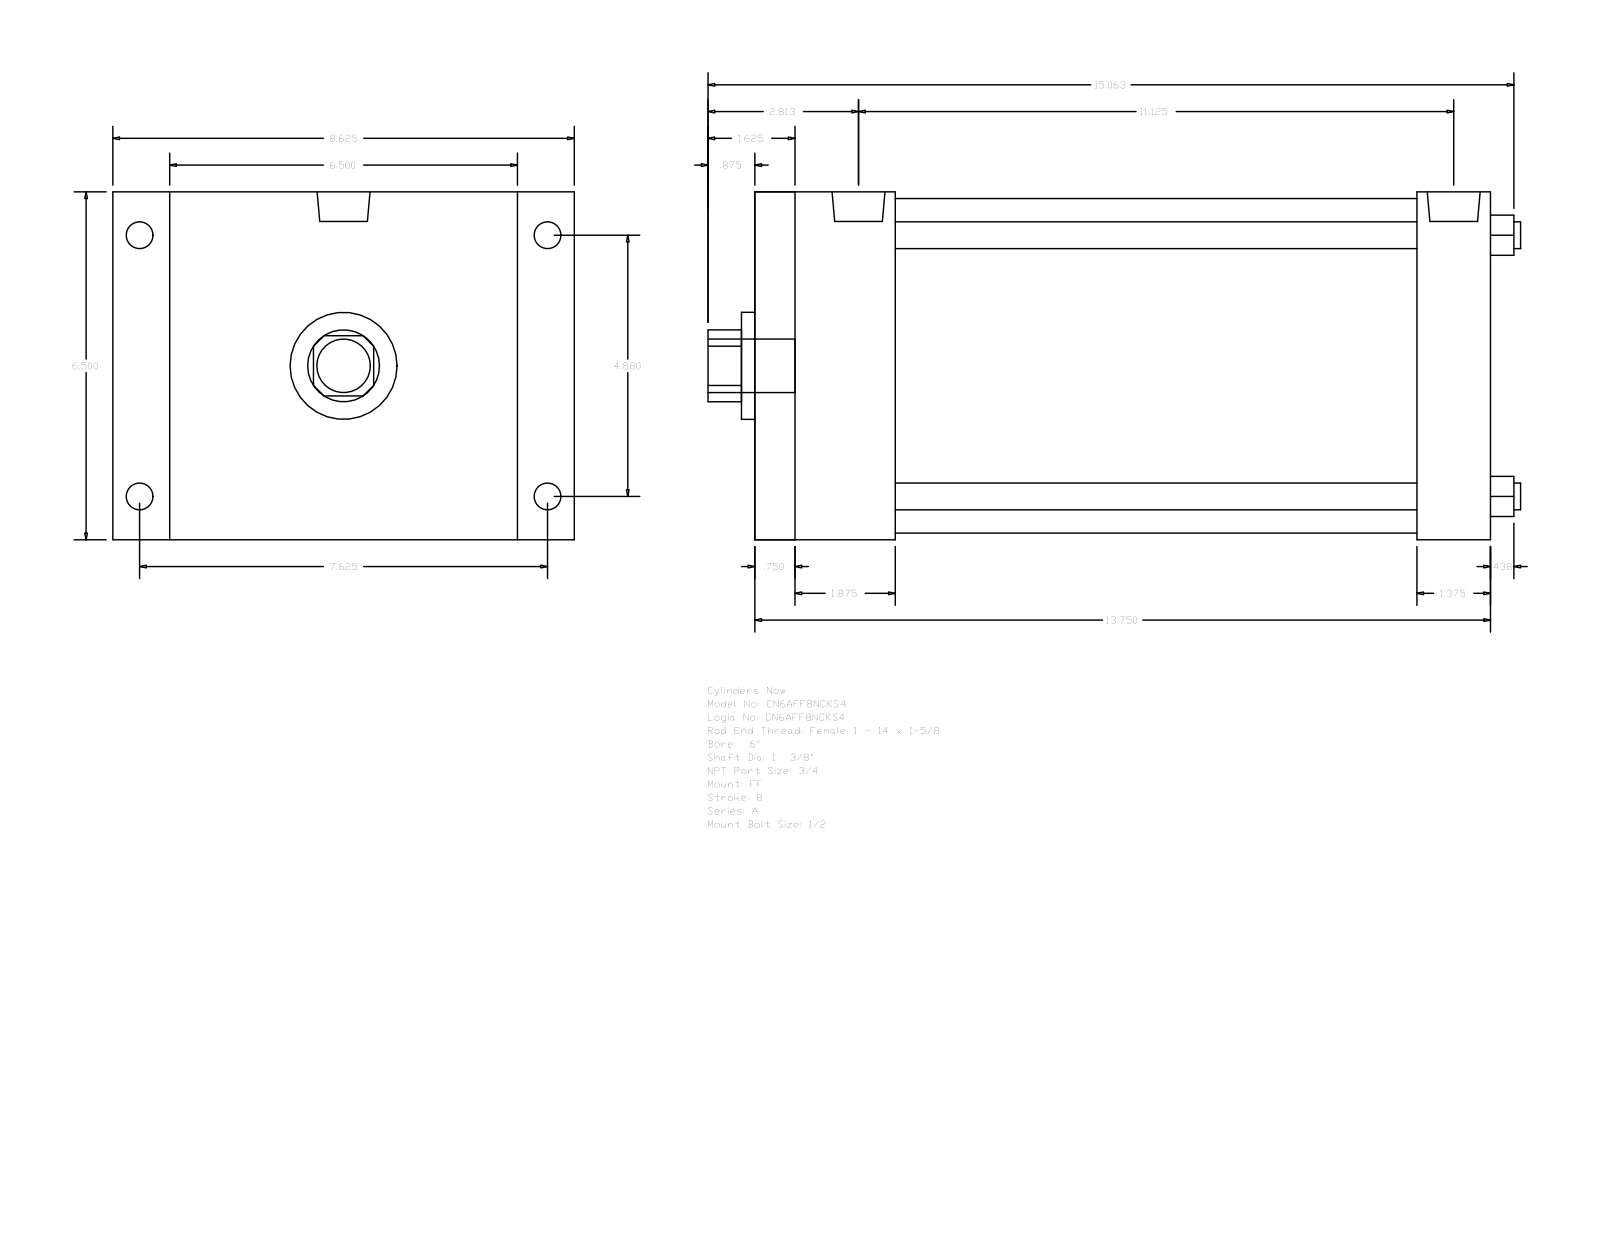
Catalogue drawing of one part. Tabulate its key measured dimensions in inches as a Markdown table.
| quantity | value |
| --- | --- |
| part name | A_FF__0600_1.375 |
| STEP written by | GSSL Pune (CONFIG_CONTROL_DESIGN) |
| units | inches |
| bodies | 0 solids, 92 faces (64 planar, 28 cylindrical, 0 other) |
| overall size | 15.187 × 8.625 × 6.5 |
| round holes (diameter × count) | 0.5 × 4, 1.375 × 1, 2 × 1, 6.25 × 1 |
| round bosses / shafts (diameter × count) | 0.594 × 4, 0.5 × 4, 0.989 × 2, 1 × 1 |
| partial cylindrical surfaces (radius × count) | 0.672 × 1 |
| main face-to-face distances | 6.5, 13.75, 0.75, 13, 2.625, 1.875, 11.125, 12.375, 11.625, 9.75 |
| hole center spacings | 3.451, 4.88, 6.902 |
